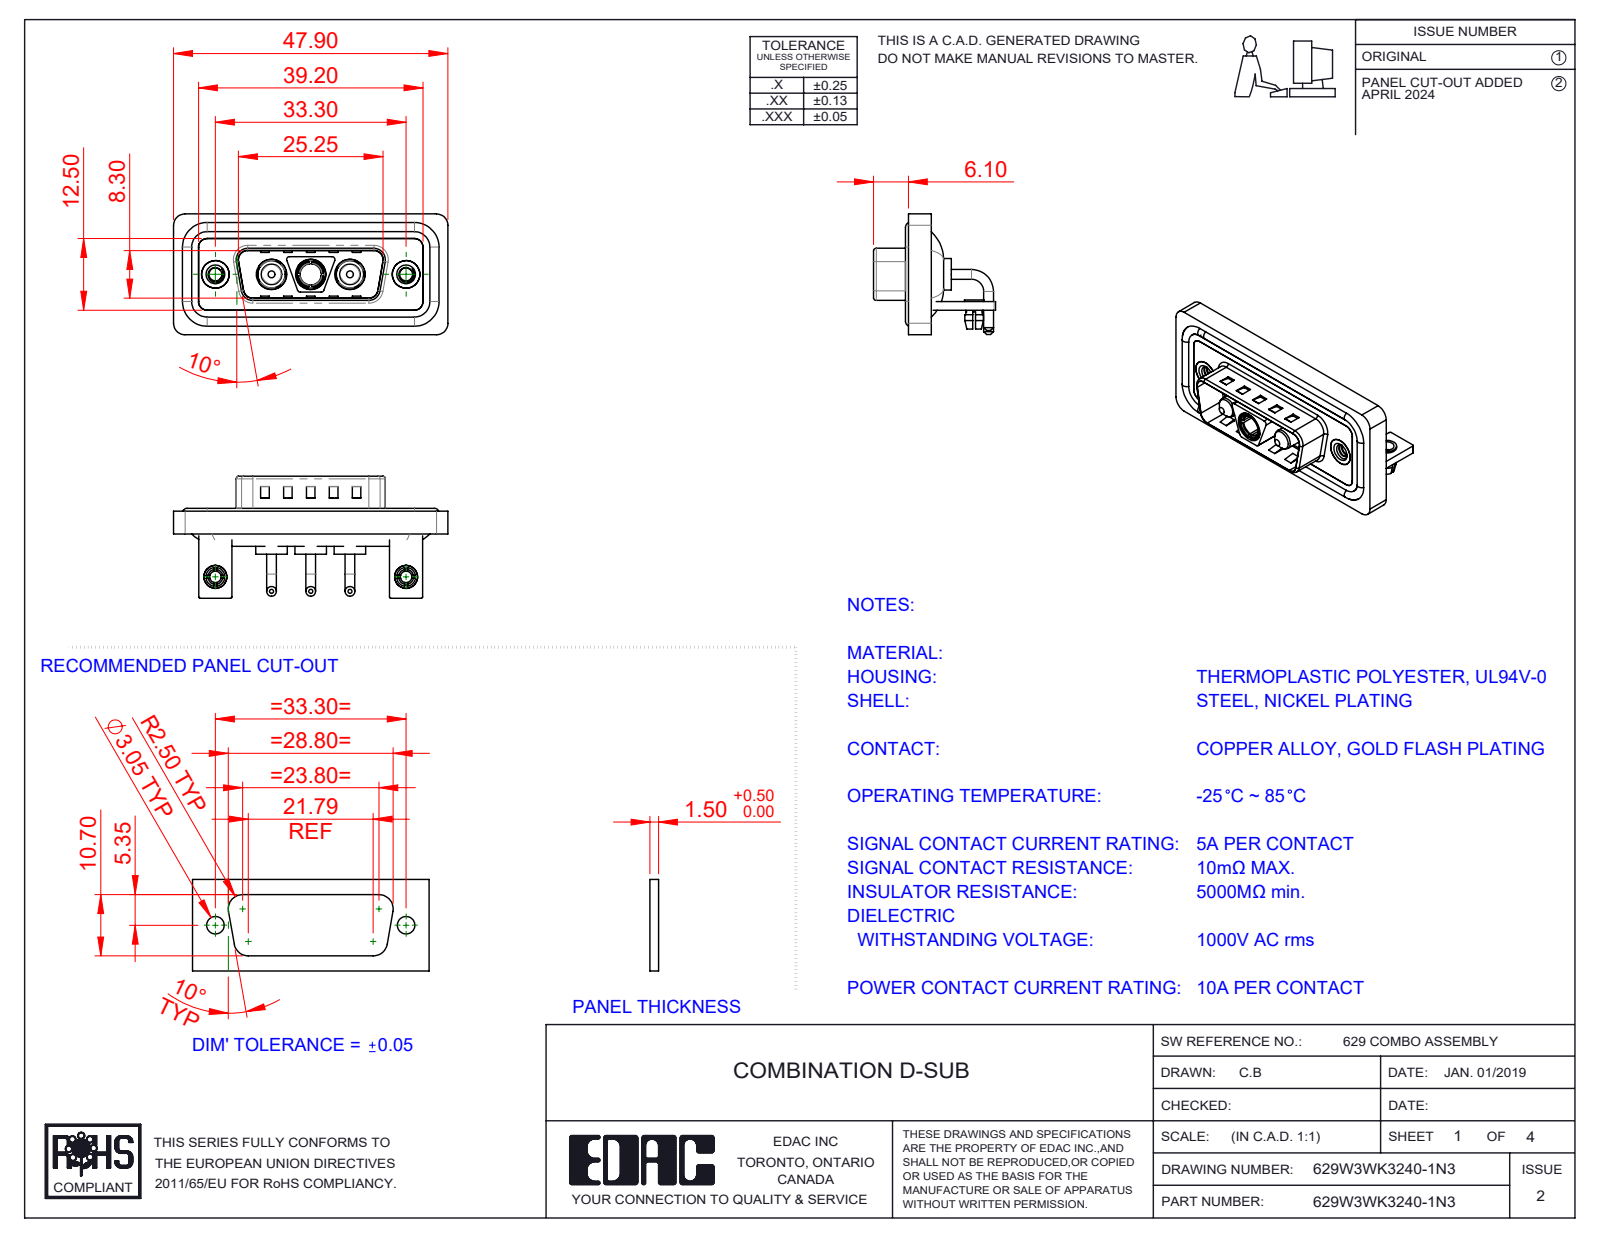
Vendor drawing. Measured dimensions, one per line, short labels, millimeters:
name: 629Combo Waterproof Housing_15 Contacts; 629Combo Threaded Rivet_3; 629Combo Shell Rear_15 Contacts; 629Combo Stabilizer Bracket (+6 more)
written by: SolidWorks 2023 (CONFIG_CONTROL_DESIGN)
unit: mm
bodies: 17 solids, 753 faces (299 planar, 306 cylindrical, 148 other)
size: 47.9 × 21.3 × 21.1
volume: 6 022 mm³; area: 10 058 mm²
holes: 3× ⌀4.85, 3× ⌀5.3, 2× ⌀2, 2× ⌀2.26, 2× ⌀2.5, 2× ⌀3.2, 2× ⌀4, 2× ⌀4.8, 2× ⌀5, 1× ⌀3.7
bosses: 6× ⌀1.7, 4× ⌀1.6, 3× ⌀5.5, 3× ⌀5.2, 3× ⌀4.75, 3× ⌀3.75, 2× ⌀4.9, 2× ⌀4
rounds: 21× R2, 18× R1.5, 16× R0.25, 13× R0.5, 8× R1.6, 4× R0.6, 4× R0.65, 4× R0.9
face distances: 0.4, 1.5, 0.8, 2.9, 1.1, 2.1, 3.7, 1.6, 1.2, 4.5
hole spacings: 6.85, 9.8, 16.65, 23.5, 33.3, 13.7
